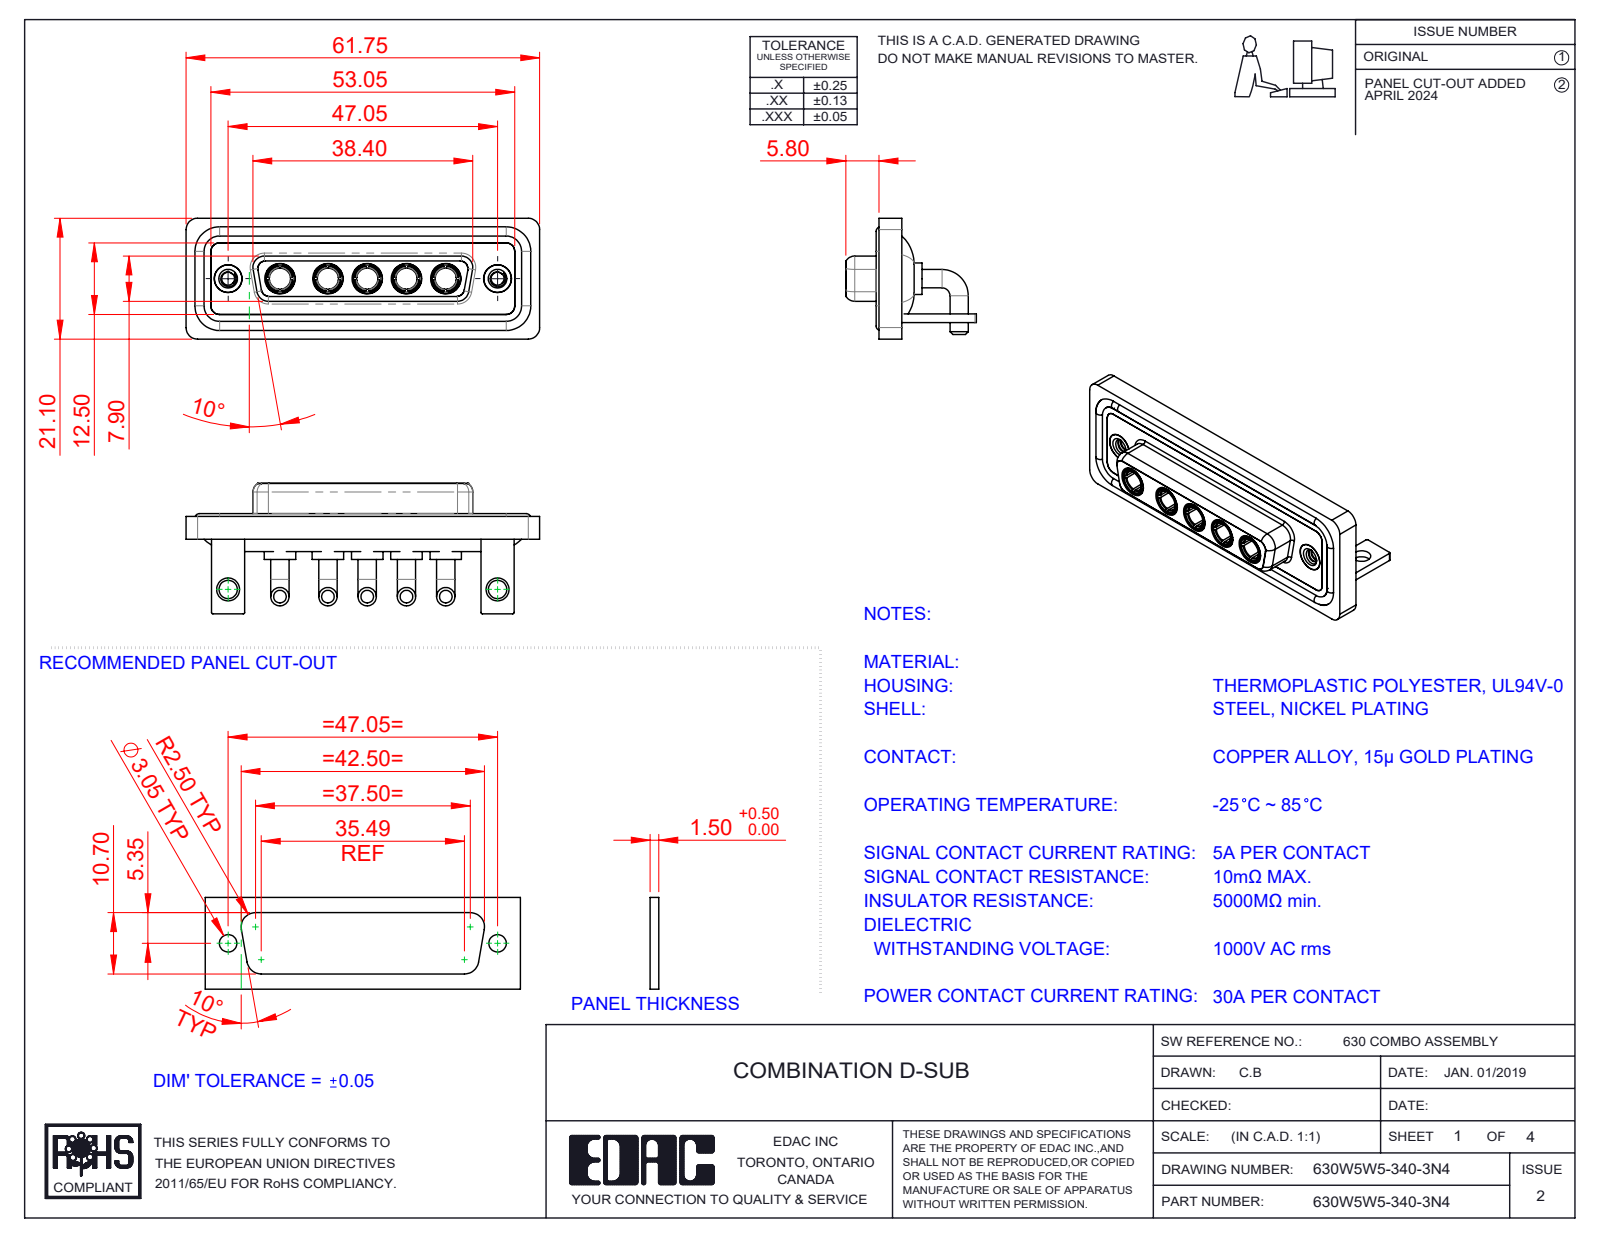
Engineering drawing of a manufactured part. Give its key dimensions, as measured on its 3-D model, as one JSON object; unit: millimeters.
{"part_name": "630Combo Threaded Rivet_2; 630Combo Waterproof Housing_25 Contacts; 630W5W5-340-3N4; 630Combo Housing_5W5 (+4 more)", "step_written_by": "SolidWorks 2023 (CONFIG_CONTROL_DESIGN)", "units": "millimeters", "bodies": {"solids": 19, "faces": 824, "planar": 270, "cylindrical": 337, "other": 217}, "overall_size": [61.75, 22.8, 21.1], "volume_mm3": 8942, "surface_area_mm2": 14641, "round_holes": [[4.85, 7], [3.7, 5], [5.3, 5], [2.26, 2], [3.2, 2], [4, 2], [4.05, 2], [5, 2]], "round_bosses_or_shafts": [[3.2, 10], [5.5, 5], [5.2, 5], [4.96, 5], [4.75, 5], [3.75, 5], [1.6, 4], [4.95, 2]], "partial_cylinders_radius": [[2, 19], [1.5, 18], [0.25, 16], [1.35, 8], [1.6, 8], [0.5, 5], [2.1, 5], [0.6, 4]], "face_to_face_distances": [0.4, 1.8, 2.9, 3.7, 1.5, 4.1, 1.1, 1.4, 1.6, 2.5], "hole_center_spacings": [6.86, 9.04, 38.01, 47.05, 6.87, 8.38, 13.72, 13.73]}
